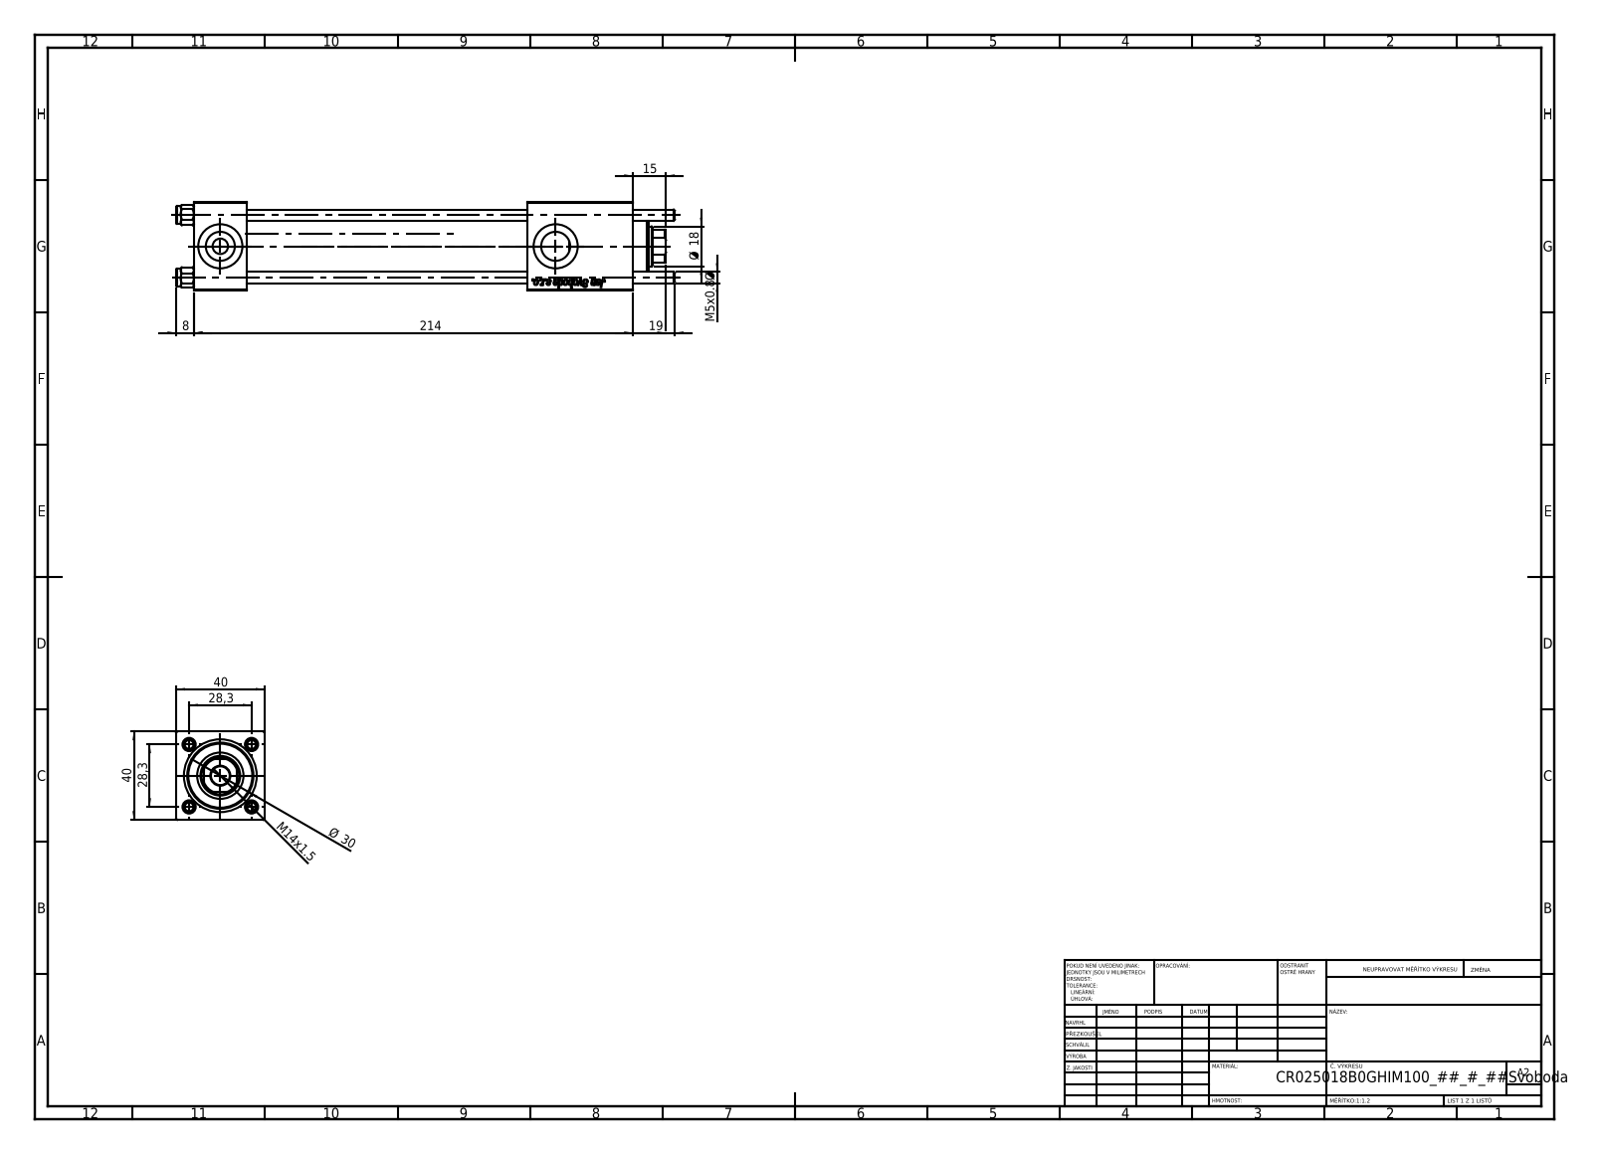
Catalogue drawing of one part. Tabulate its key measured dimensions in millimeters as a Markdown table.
| quantity | value |
| --- | --- |
| part name | NUT_M5_B; V215CR_VCP_B; V215CR_B-1; V215CR_B_TYCINKA (+1 more) |
| STEP written by | SolidWorks 2019 (CONFIG_CONTROL_DESIGN) |
| units | millimeters |
| bodies | 11 solids, 1152 faces (428 planar, 76 cylindrical, 648 other) |
| overall size | 226 × 40 × 40 |
| volume | 200 243 mm³ |
| surface area | 84 519 mm² |
| round holes (diameter × count) | 5 × 4, 20 × 3, 7 × 2, 13.16 × 2, 8.5 × 1, 18 × 1, 21 × 1, 25 × 1, 30 × 1 |
| round bosses / shafts (diameter × count) | 8 × 4, 31 × 1 |
| partial cylindrical surfaces (radius × count) | 8.5 × 1 |
| main face-to-face distances | 40, 24, 151, 127, 170.3, 146.3, 19.3, 199, 175, 48 |
| hole center spacings | 20.01, 28.3, 40.02, 152 |
